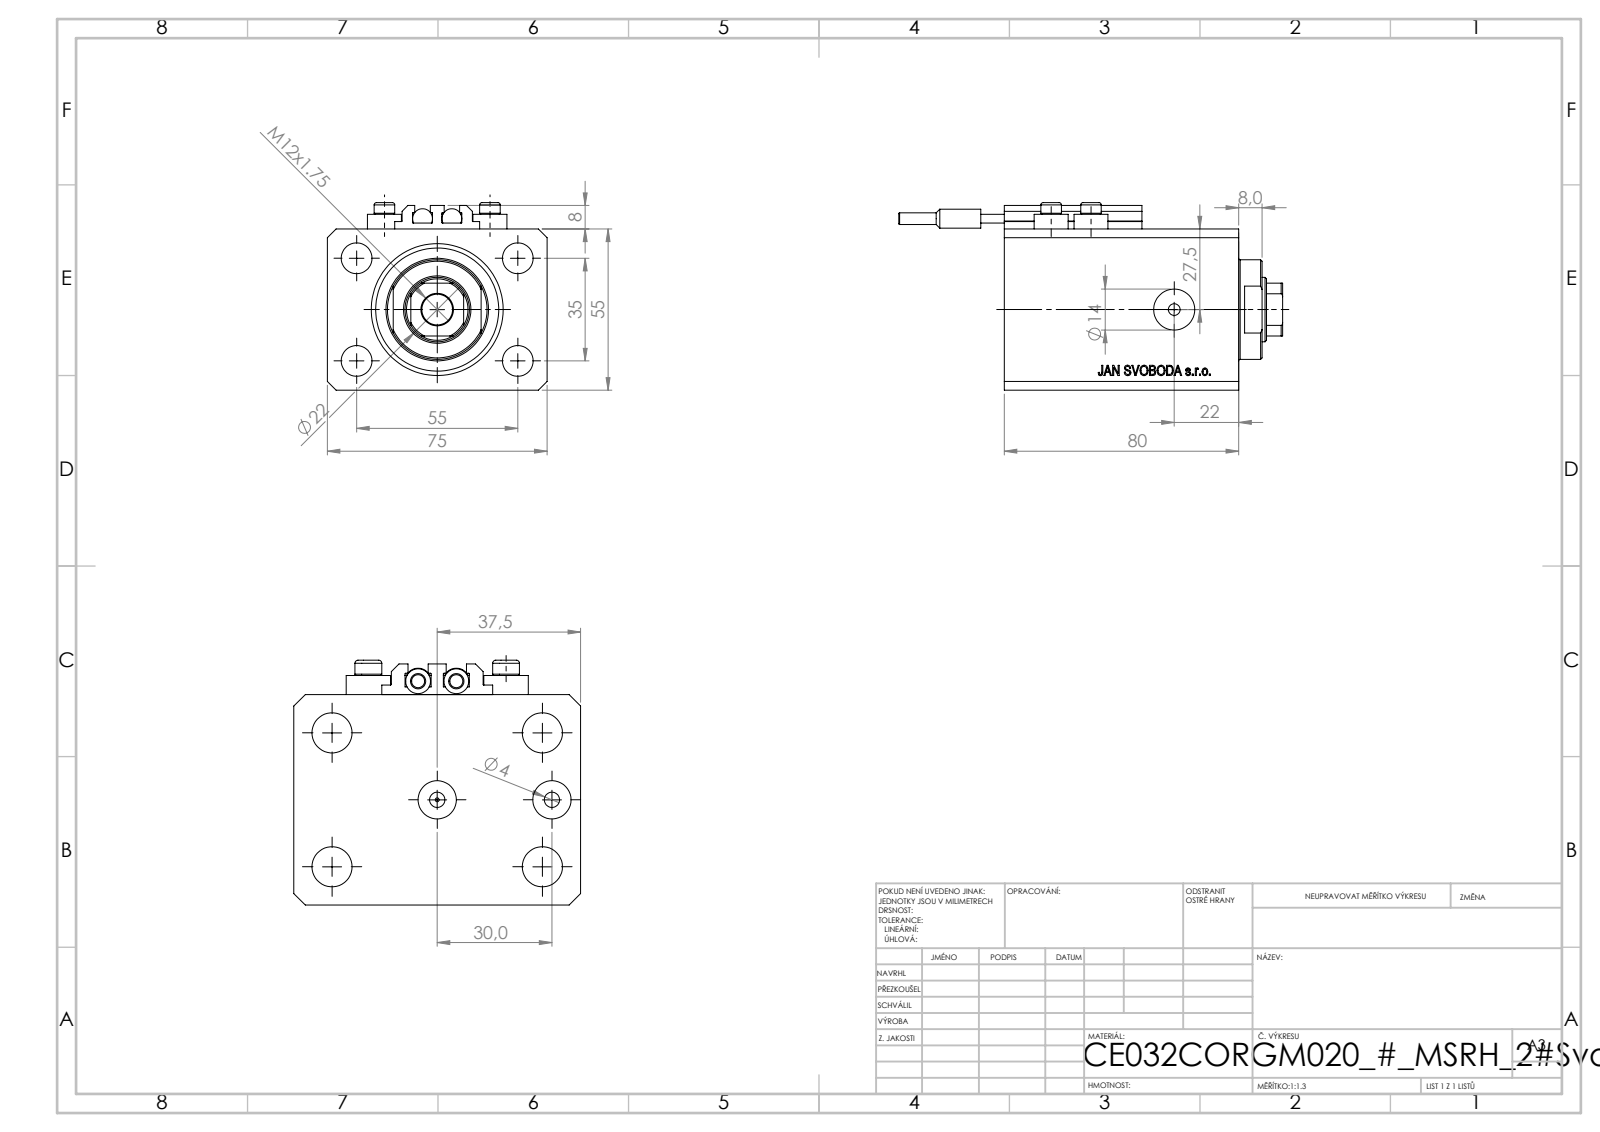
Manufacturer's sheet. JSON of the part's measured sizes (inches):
{"part_name": "SWITCH_V250CE; V250CE_C_Body; V250CE_C_VCP; ALLEN BOLT V250CE (+1 more)", "step_written_by": "SolidWorks 2019 (CONFIG_CONTROL_DESIGN)", "units": "inches", "bodies": {"solids": 10, "faces": 1094, "planar": 536, "cylindrical": 104, "other": 454}, "overall_size": [5.157, 2.953, 2.52], "volume_in3": 18.81, "surface_area_in2": 115.7, "round_holes": [[0.157, 8], [0.413, 5], [0.394, 2], [0.551, 2], [0.049, 1], [0.866, 1], [1.26, 1], [1.772, 1]], "round_bosses_or_shafts": [[0.457, 4], [0.276, 4], [0.268, 2], [0.256, 2], [0.157, 2], [1.339, 1]], "partial_cylinders_radius": [[0.008, 10], [0.413, 1]], "face_to_face_distances": [2.165, 2.953, 3.15, 0.591, 2.559, 0.39, 2.169, 2.76, 0.118, 0.079], "hole_center_spacings": [1.283, 1.417, 0.535, 0.696, 1.378, 1.515, 2.165, 2.366]}
